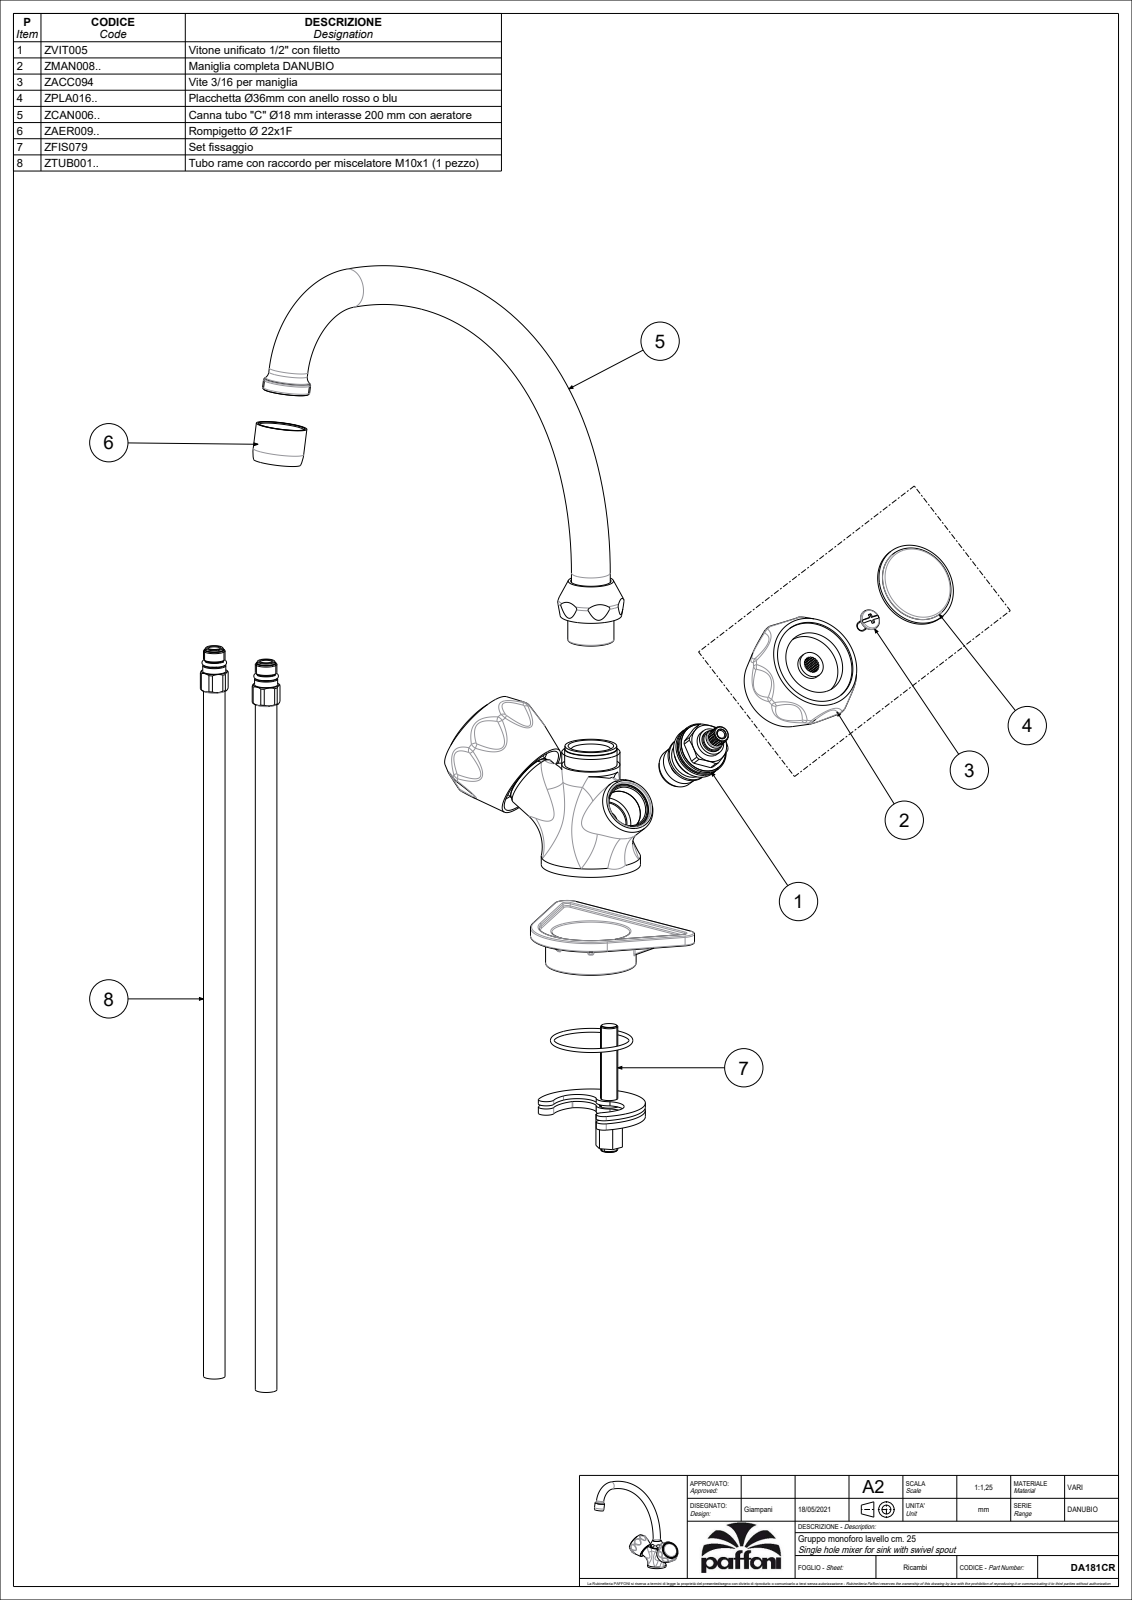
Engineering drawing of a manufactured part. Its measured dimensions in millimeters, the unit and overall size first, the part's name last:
Units: millimetres
Overall size (bounding box): 245.9 × 236.31 × 145.89
Round holes (diameter × count): ⌀9 ×4, ⌀11 ×2, ⌀18 ×2, ⌀19 ×2, ⌀21.5 ×2, ⌀22 ×2, ⌀6 ×1, ⌀6.8 ×1, ⌀12 ×1, ⌀16.3 ×1, ⌀16.4 ×1, ⌀18.1 ×1
Round bosses / shafts (diameter × count): ⌀38.5 ×2, ⌀26 ×2, ⌀18 ×2, ⌀46 ×1, ⌀34 ×1, ⌀27 ×1, ⌀24 ×1, ⌀23.6 ×1
Partial cylindrical surfaces — rounded edges, fillets, slot ends (radius × count): R21.31 ×16, R18.5 ×1
Main face-to-face distances: 35.3, 0.4, 35.7, 56, 55.6, 20.3, 1.3, 66.07, 64.77, 55
Hole centre spacings: 7, 13.89, 12, 14
Volume: 262 636 mm³ · Surface area: 59 065 mm²
Bodies: 1 solid, 363 faces (38 planar, 98 cylindrical, 227 other)
Part name (STEP PRODUCT): DA181CR
STEP written by: CREO PARAMETRIC BY PTC INC, 2020044 (CONFIG_CONTROL_DESIGN)
